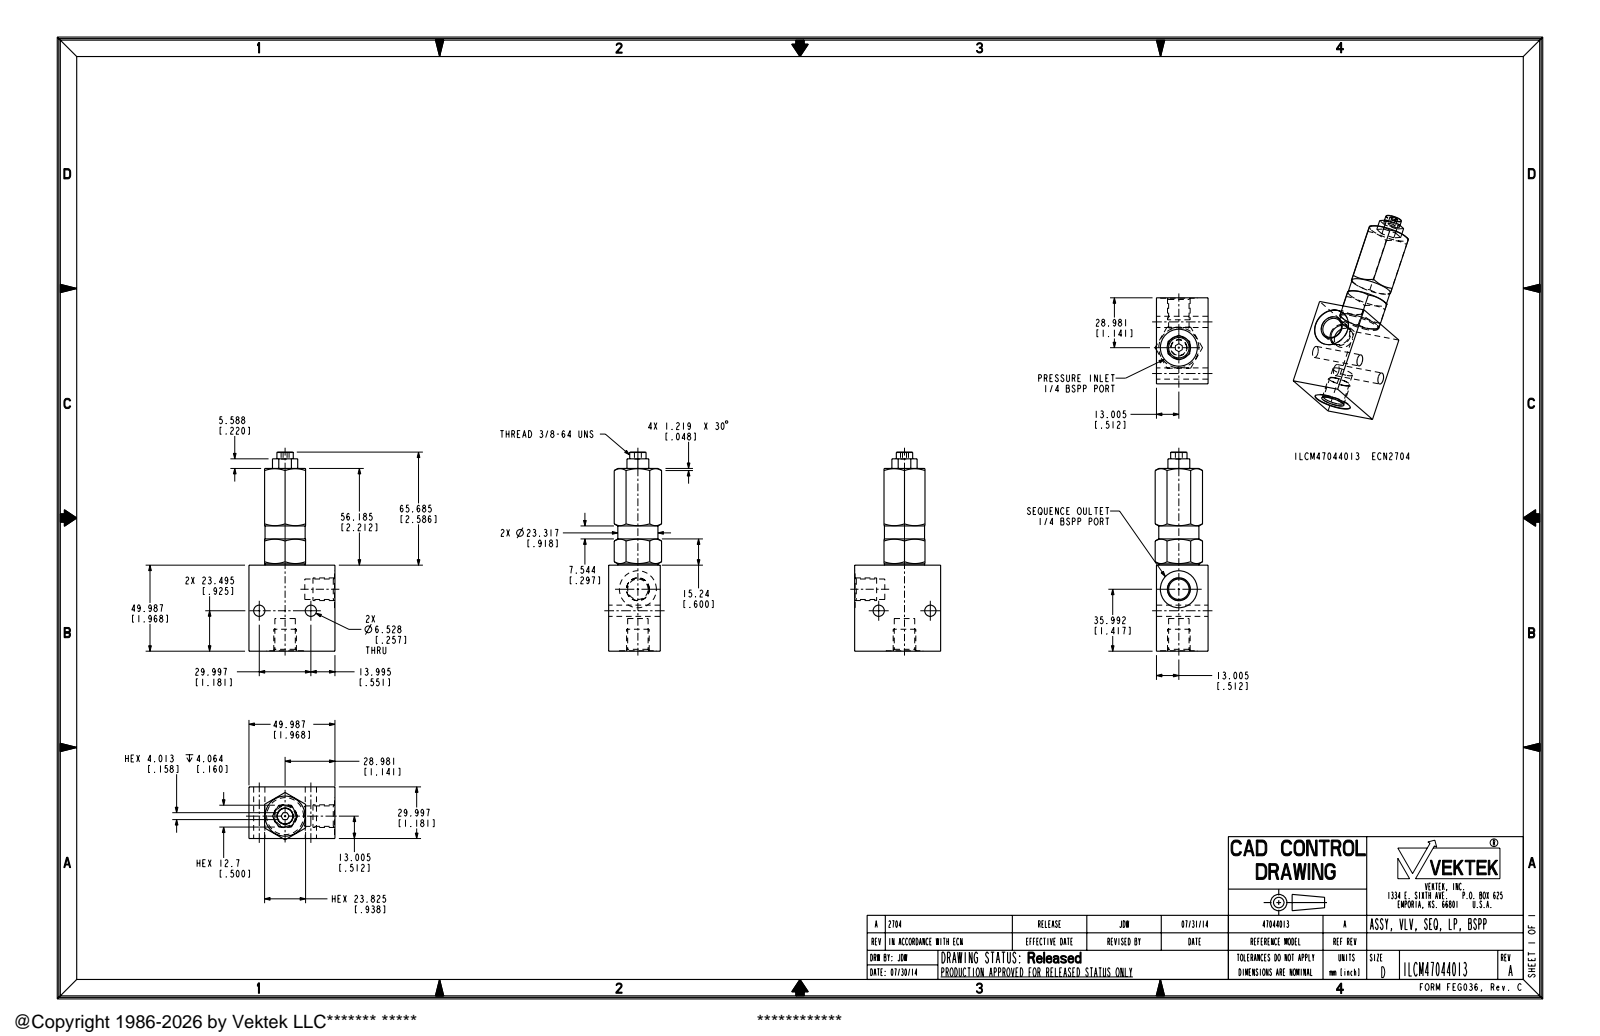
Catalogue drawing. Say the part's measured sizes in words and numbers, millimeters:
The part is named "ILCM47044013". Its 3-D file was written by "PRO/ENGINEER BY PARAMETRIC TECHNOLOGY CORPORATION, 2013320 (AUTOMOTIVE_DESIGN)". It is 1 solid with 77 faces: 41 planar, 22 cylindrical and 14 other. Overall it measures 115.67 by 49.99 by 30.75 millimeters. Its volume is 96 737 cubic millimeters and its surface area 19 628 square millimeters. Round holes: 2 of diameter 6.53, 2 of diameter 11.89, 2 of diameter 21.49. Round bosses or shafts: 2 of diameter 13.16, 1 of diameter 23.32, 1 of diameter 9.5. The main face-to-face distances are 29.99, 49.99, 23.82, 9.1, 32.92, 40.89, 17.07, 49.74, 106.17, 56.18. The hole center spacings are 30.
